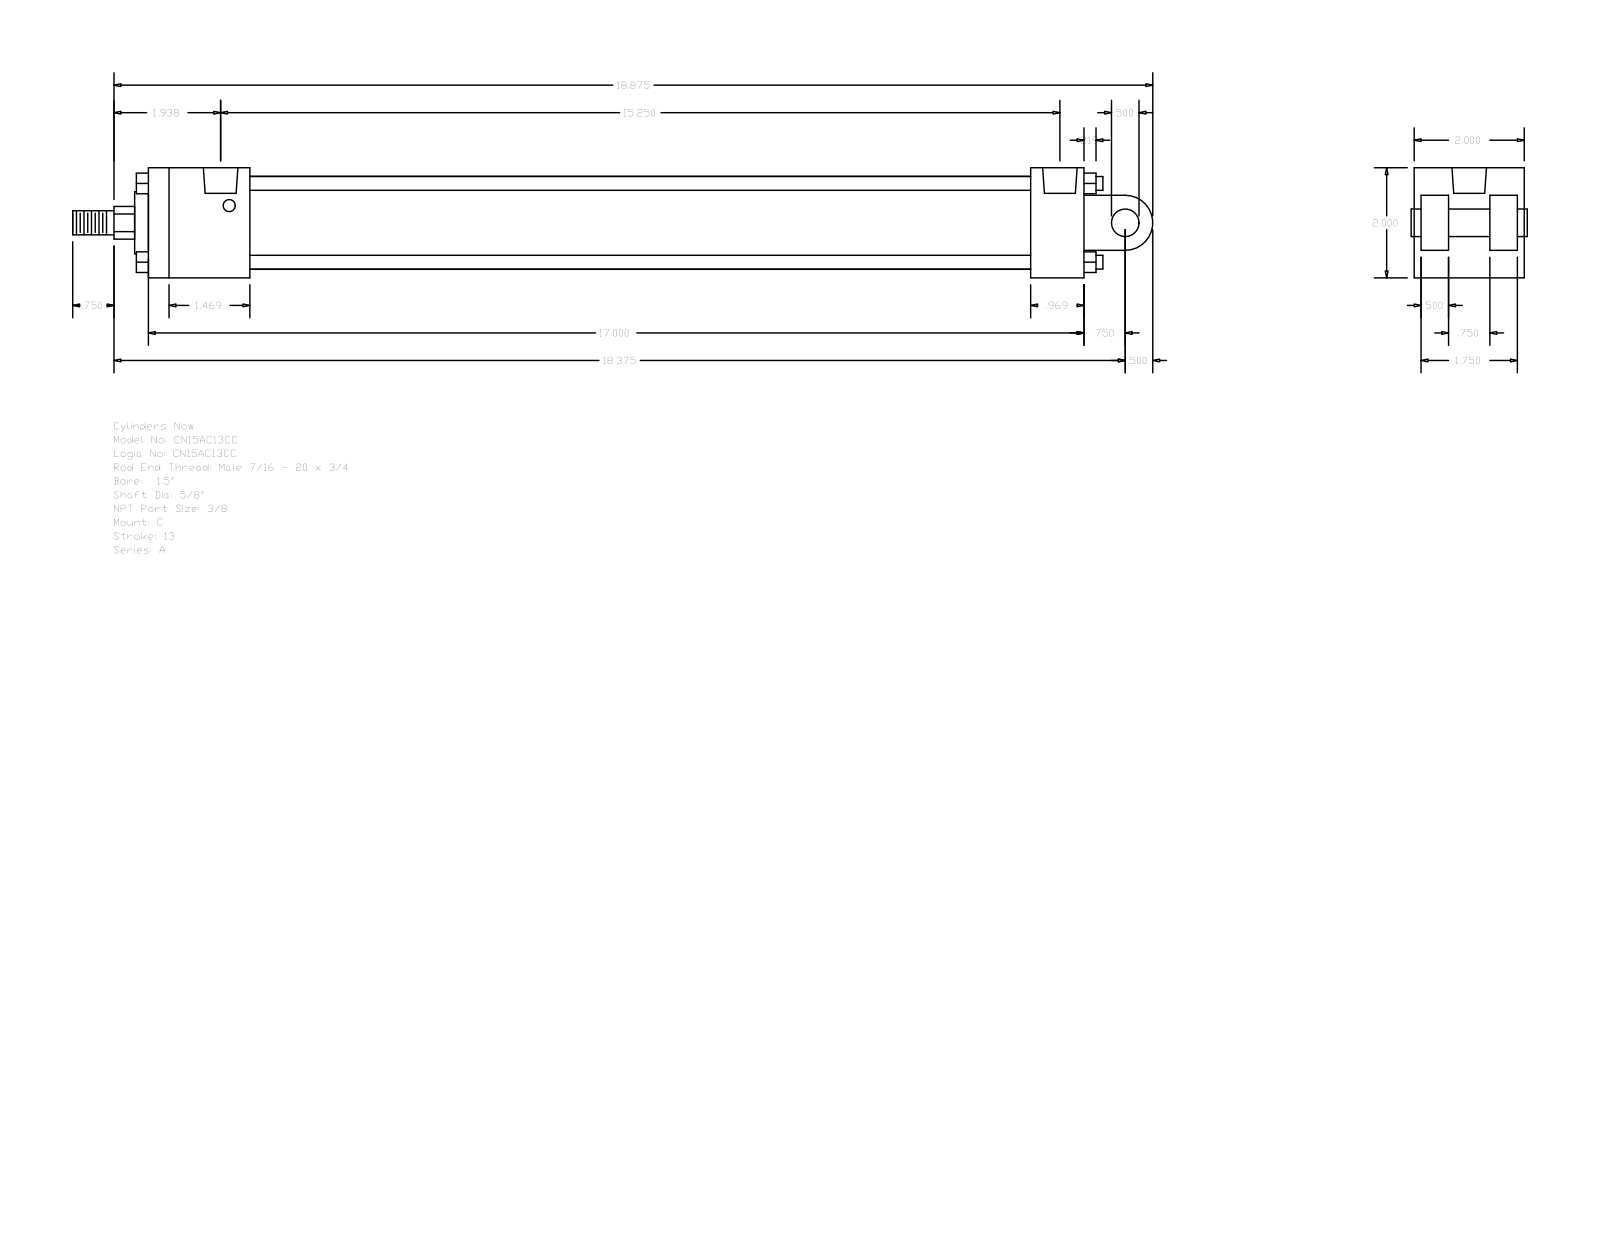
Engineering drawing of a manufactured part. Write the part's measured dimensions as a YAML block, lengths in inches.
part_name: "A_C__0150_0.625"
step_written_by: "GSSL Pune (CONFIG_CONTROL_DESIGN)"
units: inches
bodies: {solids: 0, faces: 135, planar: 102, cylindrical: 33, other: 0}
overall_size: [19.625, 2, 2]
round_holes:
  - {diameter: 0.219, count: 4}
  - {diameter: 0.627, count: 2}
round_bosses_or_shafts:
  - {diameter: 0.25, count: 4}
  - {diameter: 1.69, count: 1}
  - {diameter: 1.125, count: 1}
  - {diameter: 0.625, count: 1}
  - {diameter: 0.5, count: 1}
  - {diameter: 0.437, count: 1}
partial_cylinders:
  - {radius: 0.297, count: 1}
  - {radius: 0.5, count: 1}
face_to_face_distances: [2, 0.5, 17, 1.375, 0.125, 0.625, 1.875, 1.25, 16.031, 0.969]
hole_center_spacings: [0.156, 14.937, 15.094, 15.25]
